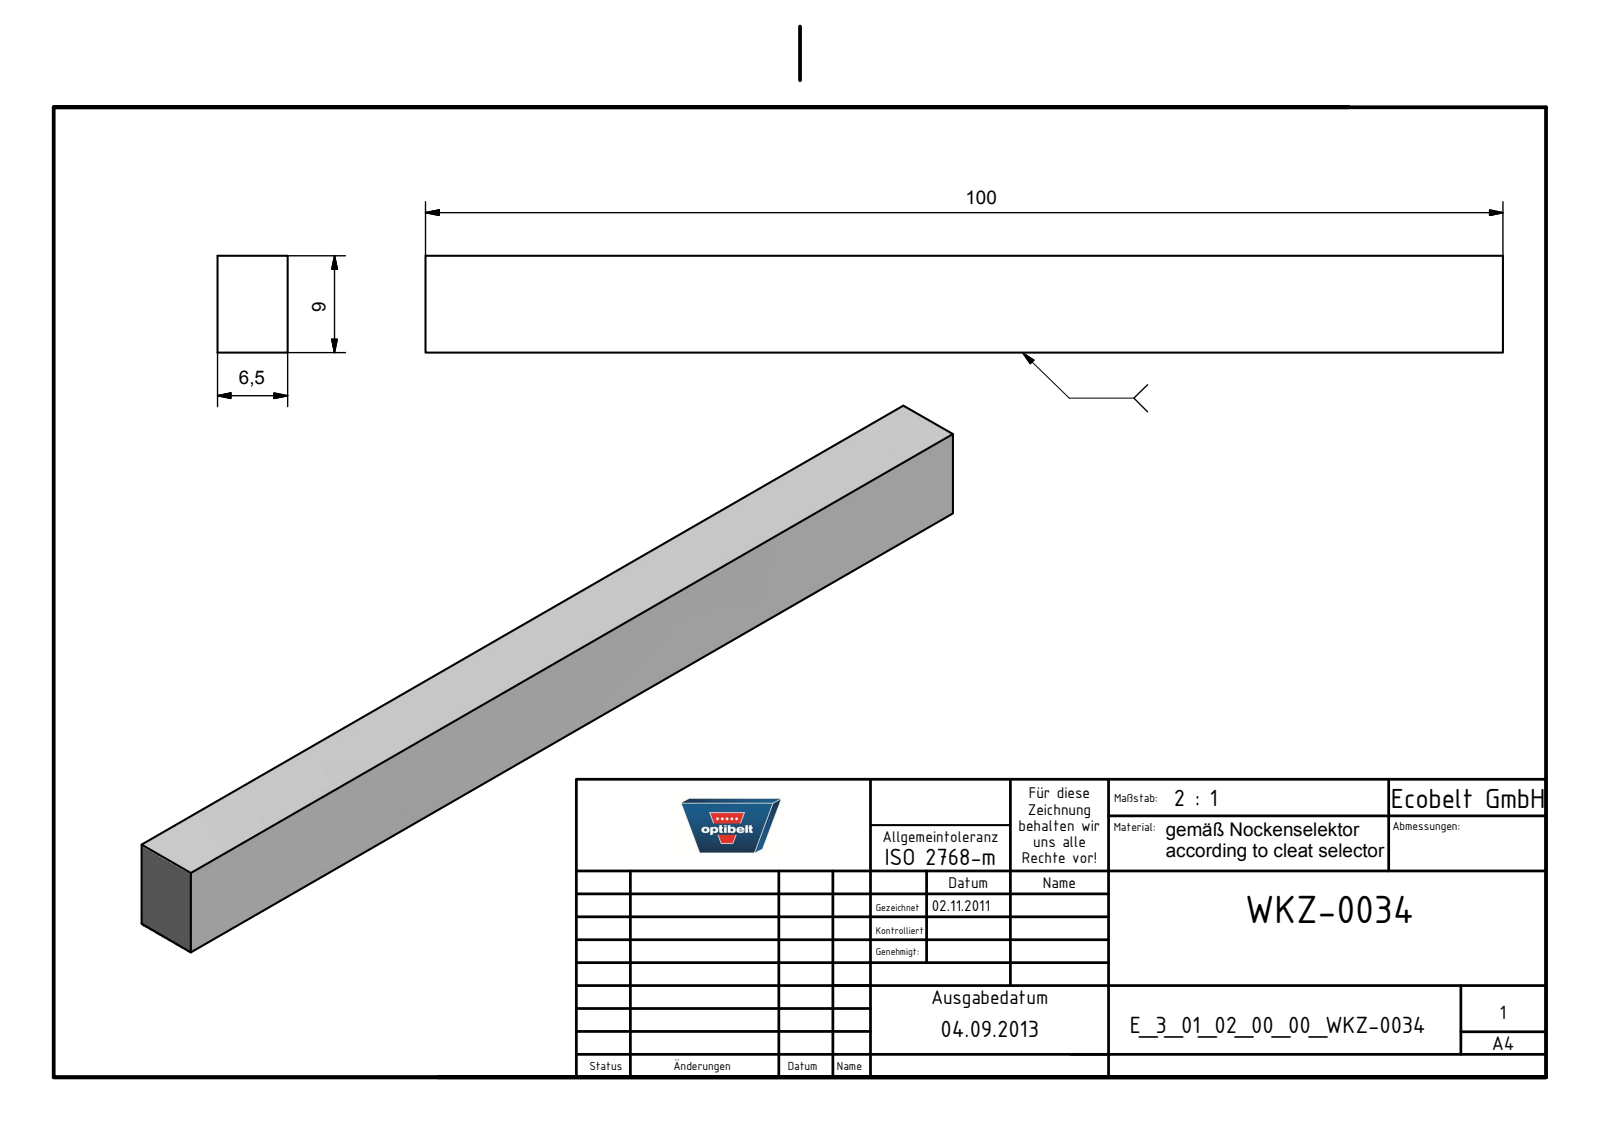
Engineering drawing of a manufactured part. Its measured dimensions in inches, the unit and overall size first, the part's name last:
Units: inches
Overall size (bounding box): 3.937 × 0.354 × 0.256
Main face-to-face distances: 0.256, 0.354, 3.937
Volume: 0.357 in³ · Surface area: 4.986 in²
Bodies: 1 solid, 6 faces (6 planar, 0 cylindrical, 0 other)
Part name (STEP PRODUCT): E_3_01_02_00_00_WKZ-0034
STEP written by: Autodesk Inventor 2021 (AUTOMOTIVE_DESIGN)
